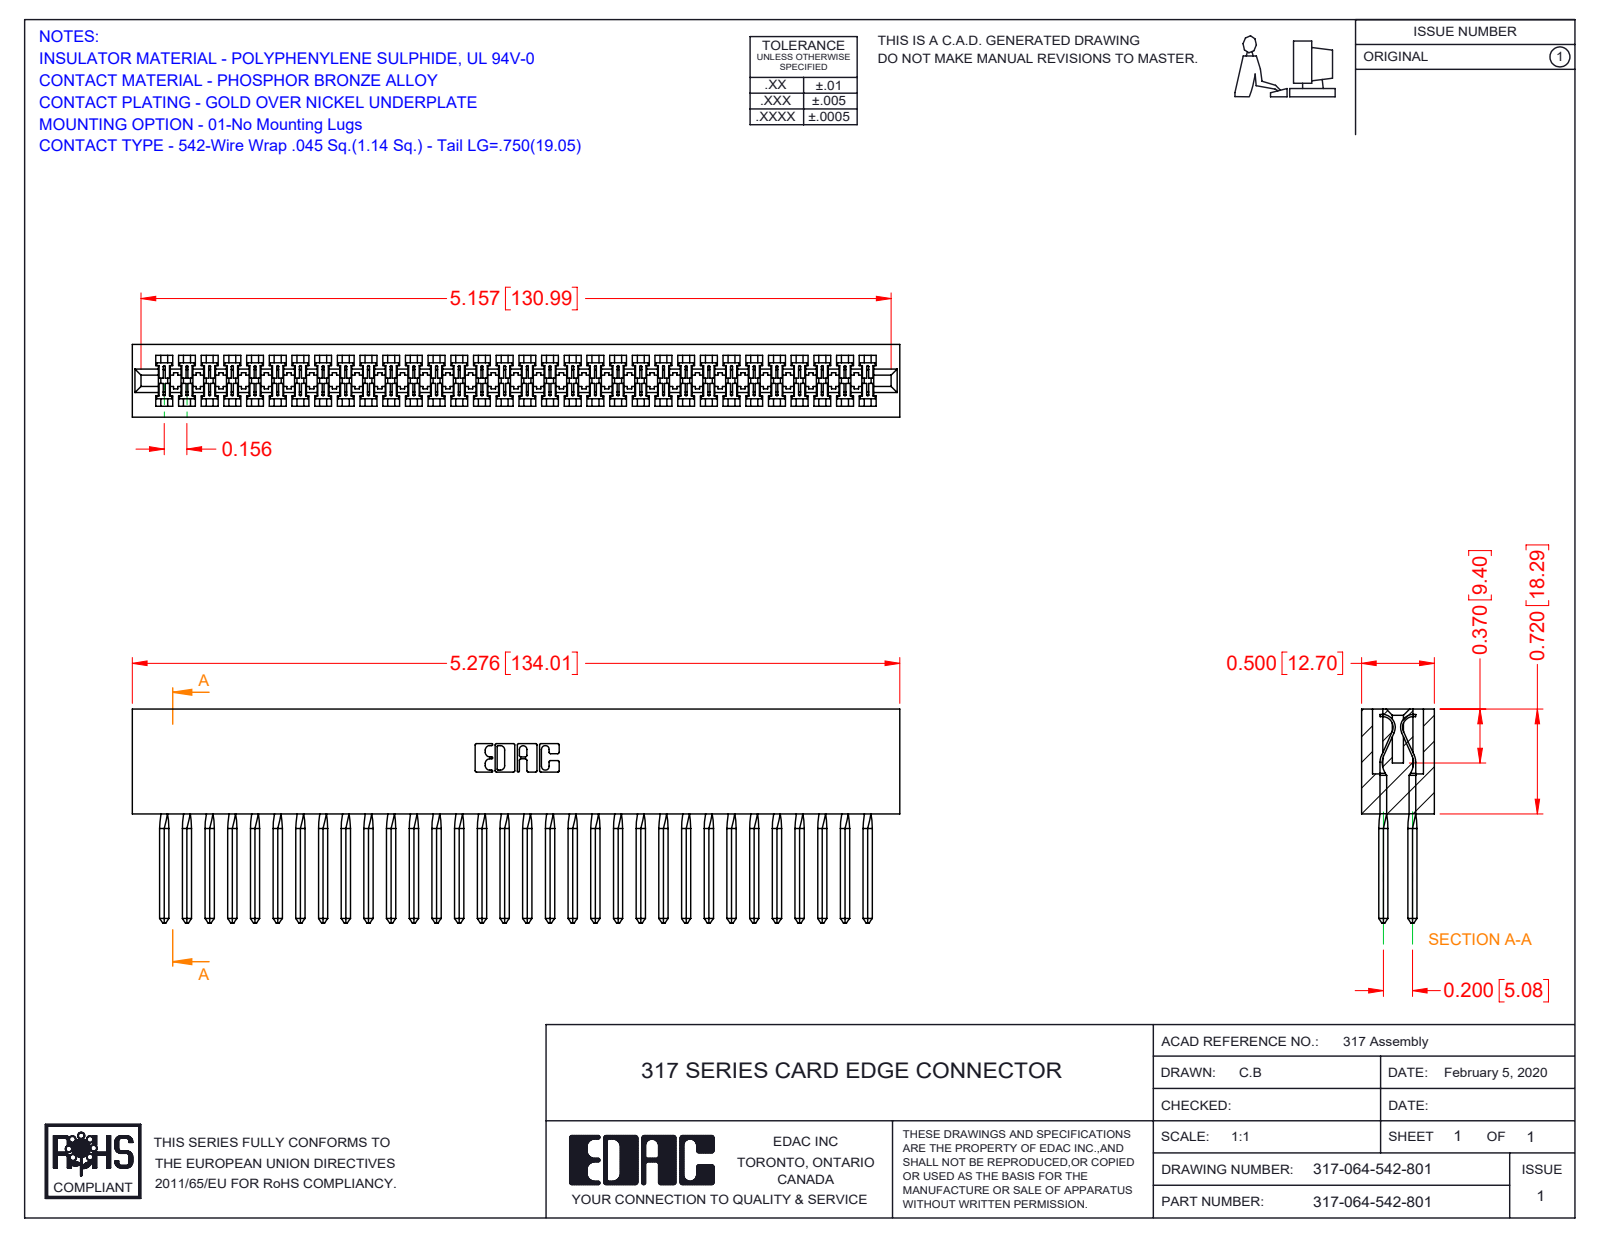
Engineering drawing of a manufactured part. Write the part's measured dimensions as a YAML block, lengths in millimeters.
part_name: "317-290-003_542; 317-064-542-801; 317 Part_Lugless"
step_written_by: "SolidWorks 2016 (CONFIG_CONTROL_DESIGN)"
units: millimeters
bodies: {solids: 65, faces: 3738, planar: 2994, cylindrical: 488, other: 256}
overall_size: [134, 37.3, 12.7]
volume: 23350
surface_area: 32340
partial_cylinders:
  - {radius: 0.2, count: 128}
  - {radius: 0.3, count: 22}
  - {radius: 0.2, count: 6}
  - {radius: 0.8, count: 6}
  - {radius: 0.7, count: 3}
  - {radius: 1.9, count: 2}
  - {radius: 2.3, count: 2}
  - {radius: 2.5, count: 2}
face_to_face_distances: [12.7, 1.9, 10.8, 8.9, 5.1, 2.9, 2.8, 1.2, 3.3, 9.4]
